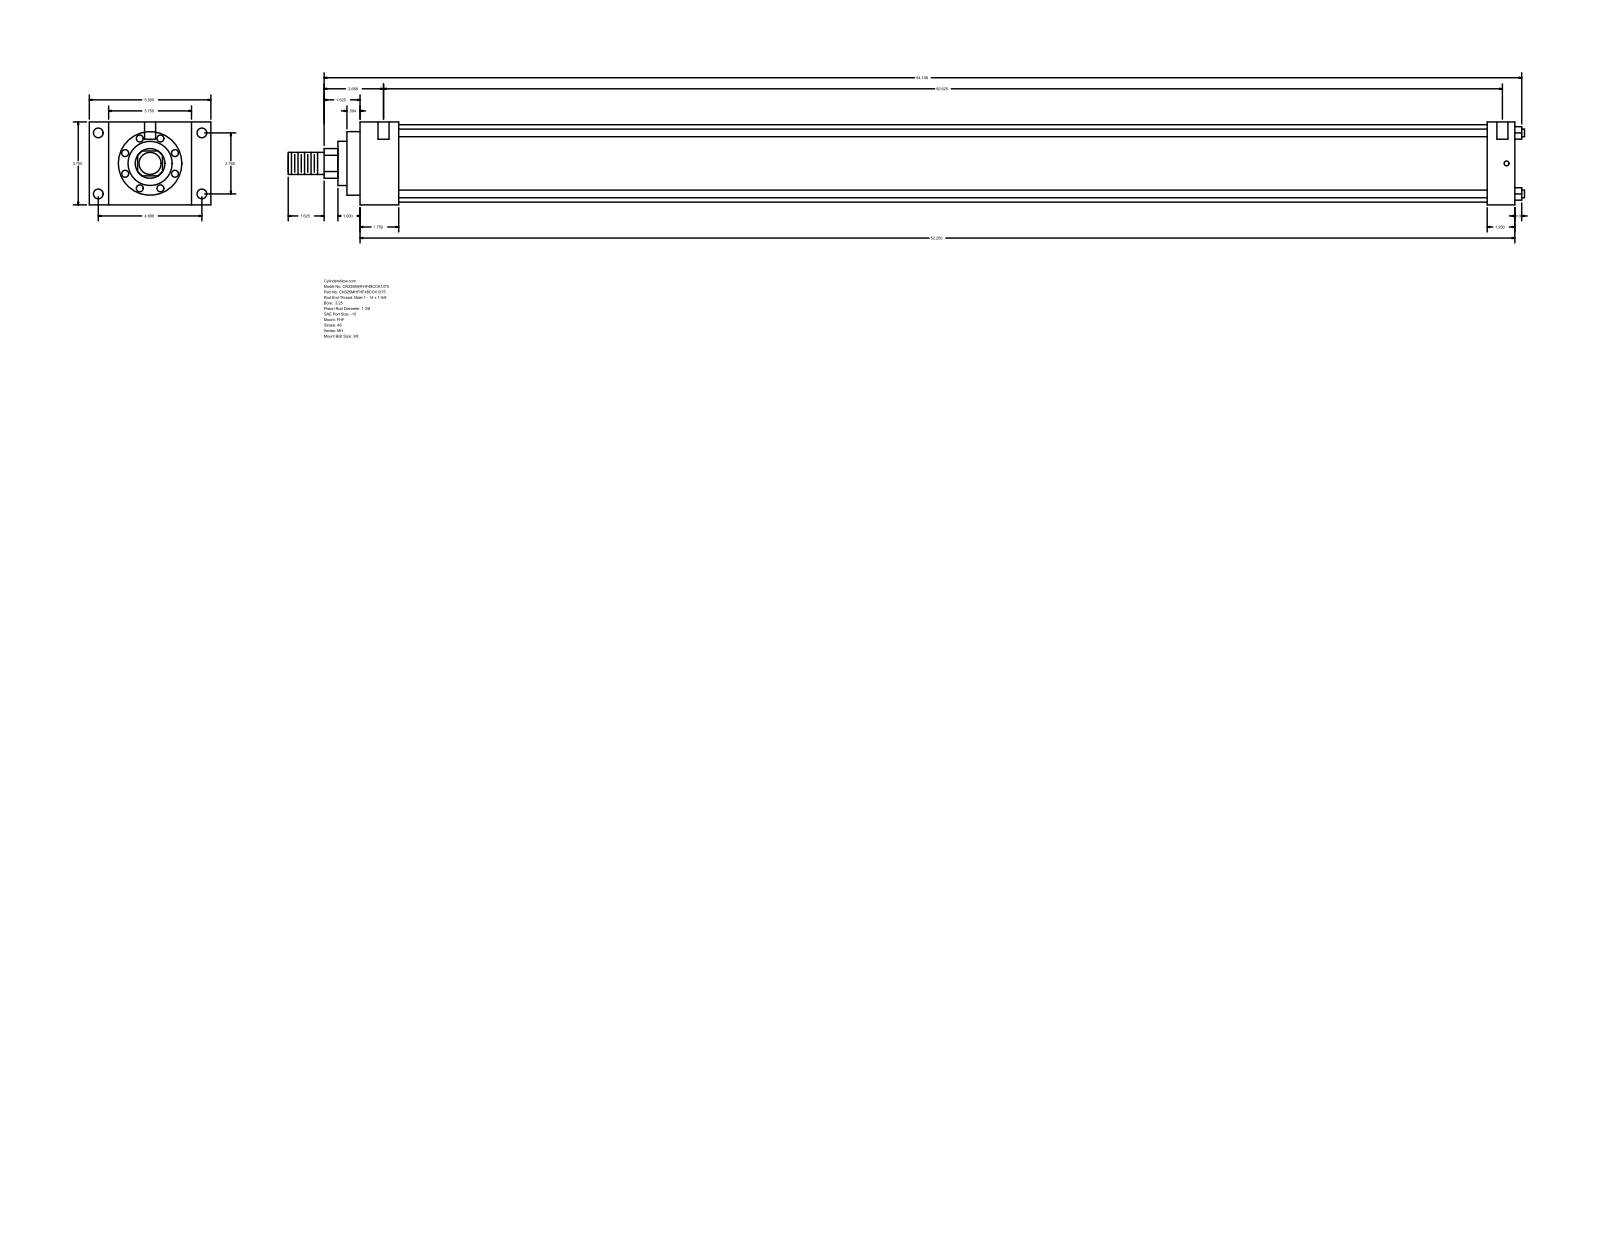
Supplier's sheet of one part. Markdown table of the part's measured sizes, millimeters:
| quantity | value |
| --- | --- |
| part name | MH_FHF__0325_1.375 |
| STEP written by | GSSL Pune (CONFIG_CONTROL_DESIGN) |
| units | millimeters |
| bodies | 0 solids, 90 faces (61 planar, 29 cylindrical, 0 other) |
| overall size | 1420.81 × 139.7 × 95.25 |
| round holes (diameter × count) | 5.56 × 4, 11.13 × 4, 12.7 × 2 |
| round bosses / shafts (diameter × count) | 8.76 × 4, 88.9 × 1, 73.03 × 1, 50.8 × 1, 34.92 × 1, 25.4 × 1 |
| partial cylindrical surfaces (radius × count) | 17.06 × 1 |
| main face-to-face distances | 95.24, 1327.15, 44.45, 1282.7, 22.23, 117.47, 139.7, 1295.4, 1250.95, 31.75 |
| hole center spacings | 70.1, 119.06, 138.16, 1292.23, 1.59, 4.76, 1285.88, 1287.47 |
